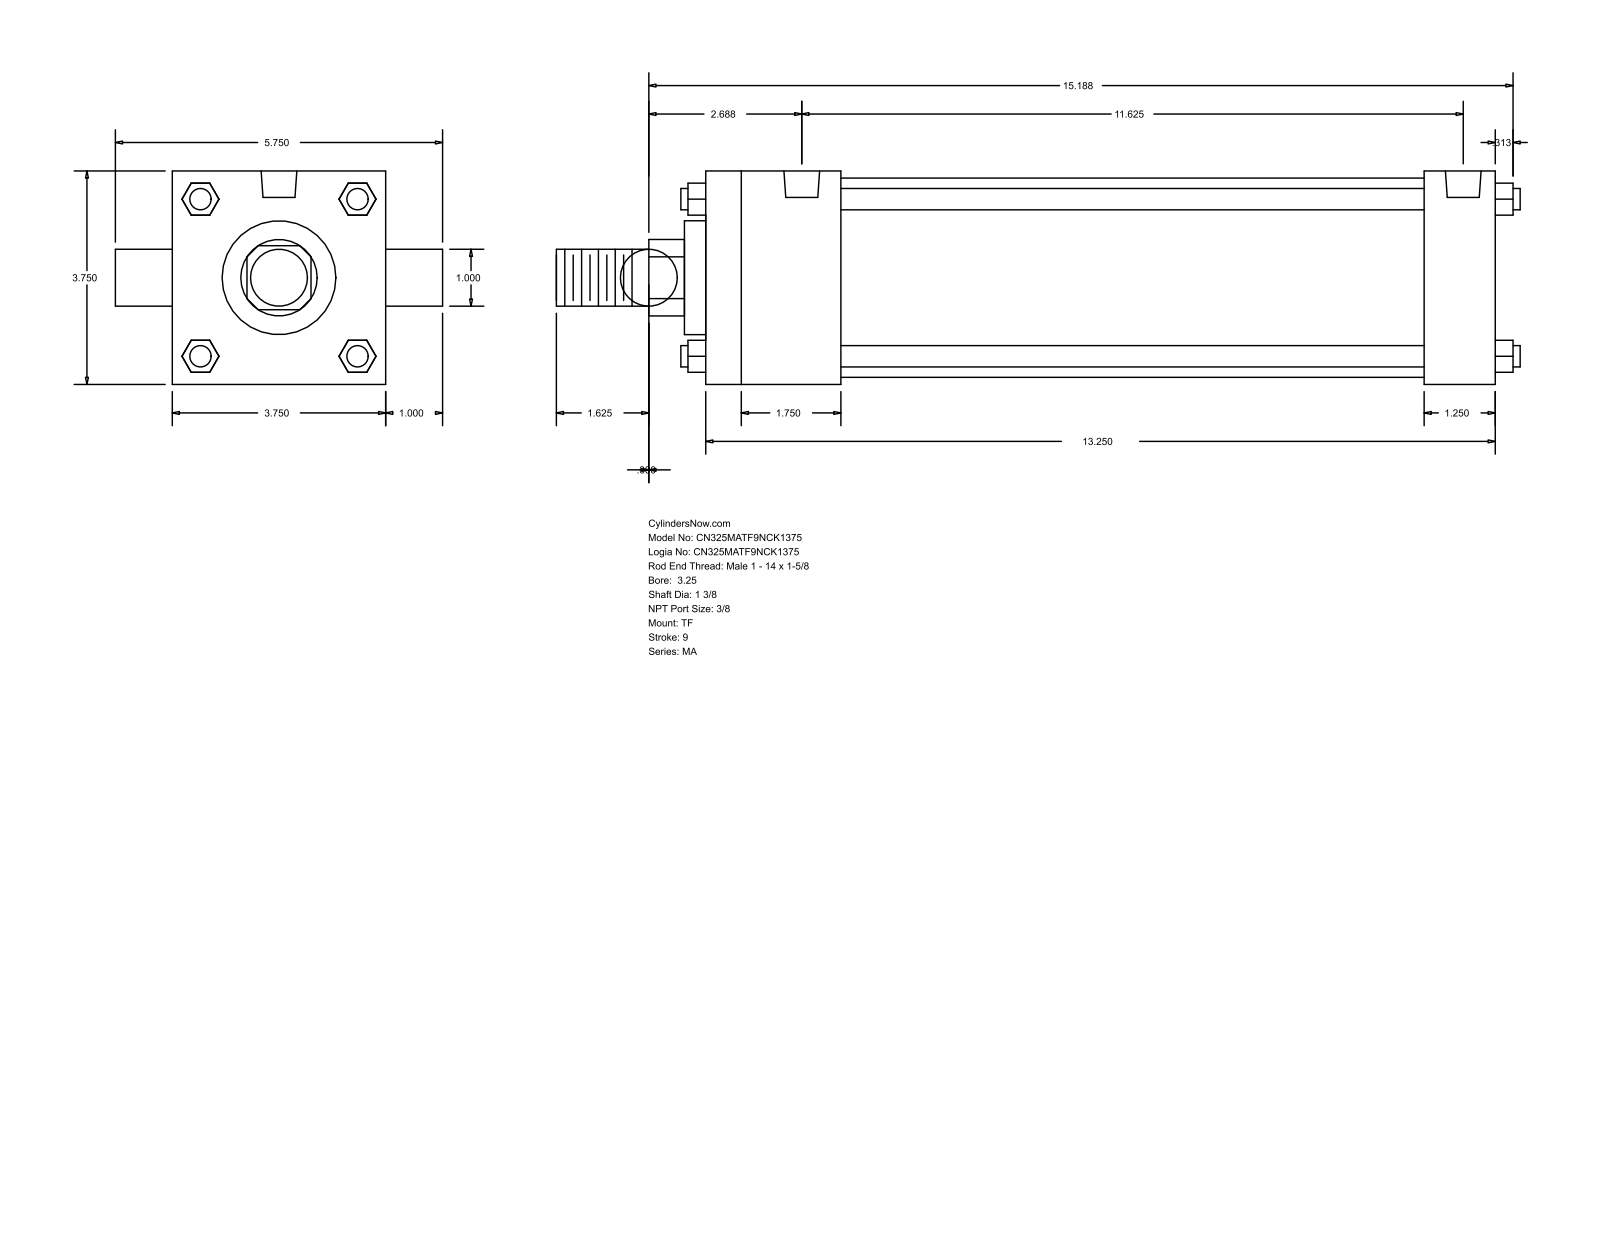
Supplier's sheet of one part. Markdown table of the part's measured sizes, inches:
| quantity | value |
| --- | --- |
| part name | MA_TF__0325_1.375 |
| STEP written by | GSSL Pune (CONFIG_CONTROL_DESIGN) |
| units | inches |
| bodies | 0 solids, 120 faces (92 planar, 28 cylindrical, 0 other) |
| overall size | 16.937 × 5.75 × 3.75 |
| round holes (diameter × count) | 0.437 × 3, 0.627 × 2 |
| round bosses / shafts (diameter × count) | 0.375 × 4, 1 × 2, 3.5 × 1, 2 × 1, 1.375 × 1 |
| partial cylindrical surfaces (radius × count) | 0.672 × 1 |
| main face-to-face distances | 3.75, 13.875, 2.375, 12.625, 10.25, 11.5, 1.25, 0.375, 2.75, 13 |
| hole center spacings | 0.188, 11.437, 11.25, 11.625 |
